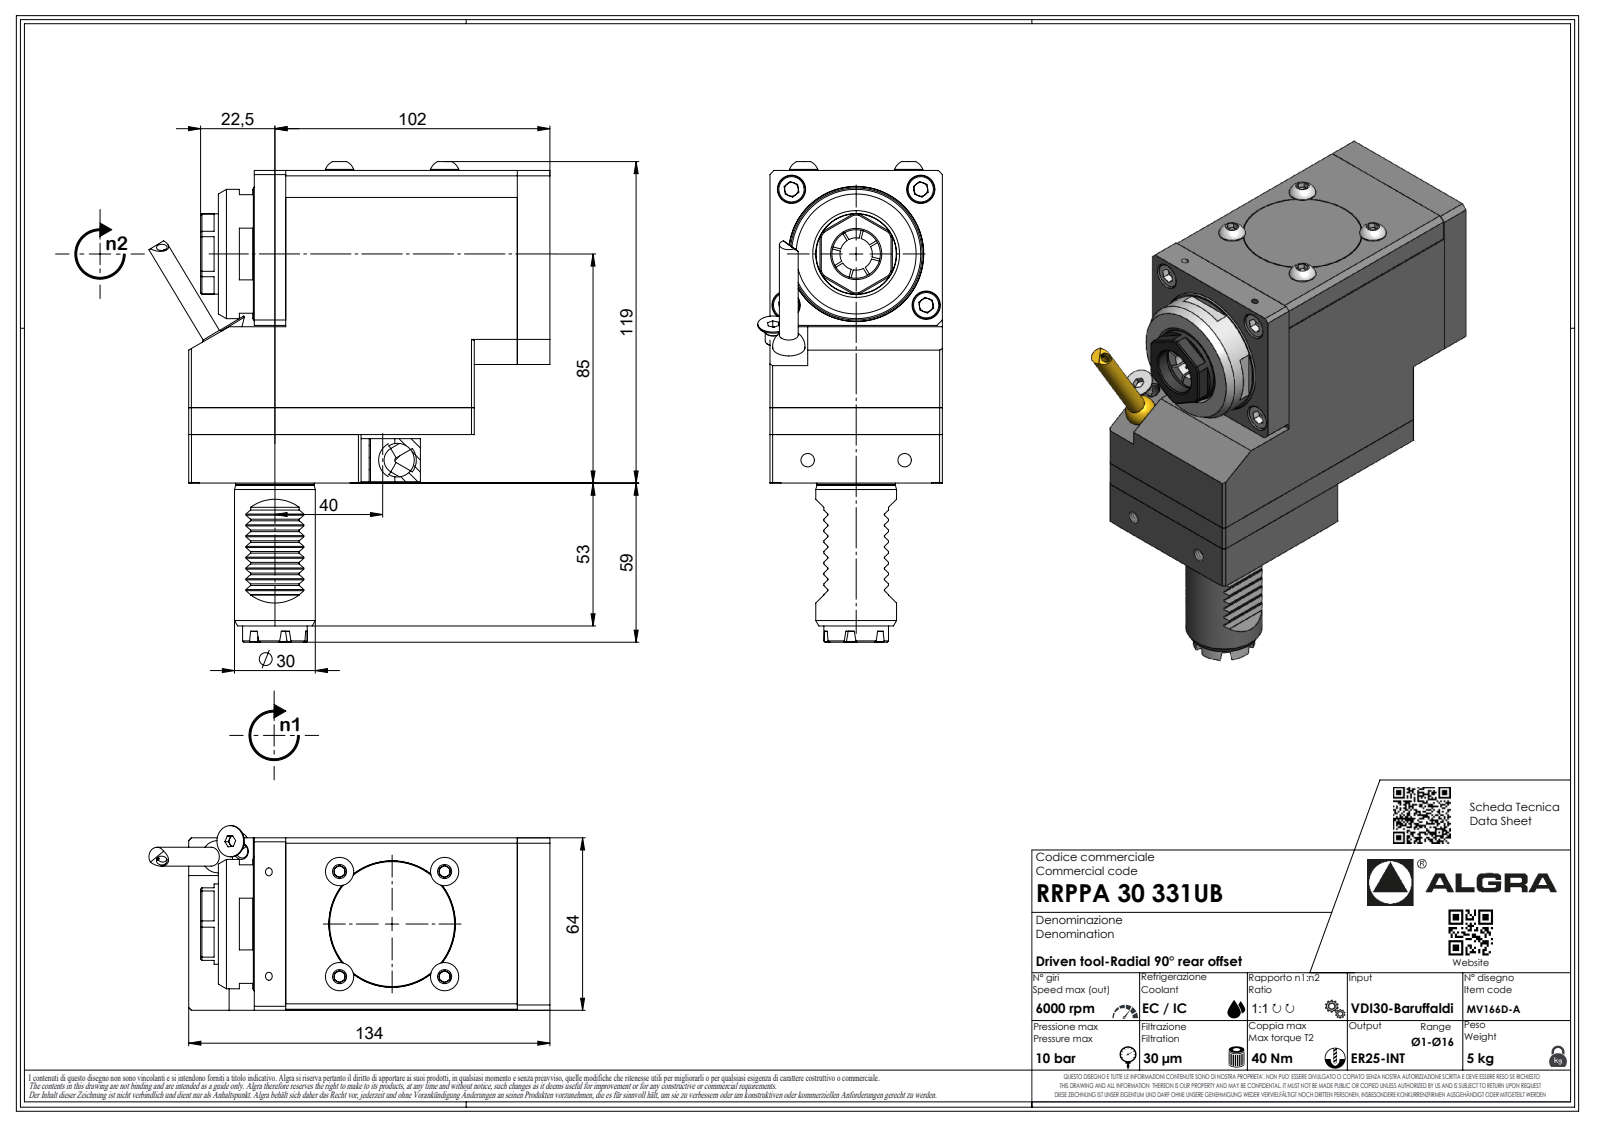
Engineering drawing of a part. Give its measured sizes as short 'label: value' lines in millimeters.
name: RRPPA30331UB
written by: SolidWorks 2023 (AUTOMOTIVE_DESIGN)
unit: mm
bodies: 1 solid, 603 faces (390 planar, 87 cylindrical, 126 other)
size: 175.06 × 148.88 × 64
volume: 838 972 mm³; area: 75 234 mm²
holes: 1× ⌀2.1, 1× ⌀4, 1× ⌀38.2, 1× ⌀42.2, 1× ⌀46.2, 1× ⌀50.2
bosses: 1× ⌀50, 1× ⌀48, 1× ⌀46, 1× ⌀42, 1× ⌀38, 1× ⌀34, 1× ⌀30, 1× ⌀29.8
rounds: 16× R0.3, 7× R0.33, 7× R0.52, 7× R3.7, 6× R0.2, 1× R0.21, 1× R2, 1× R7.6
face distances: 64, 116, 58, 134.1, 98, 18, 106, 28.1, 109.76, 81.66
